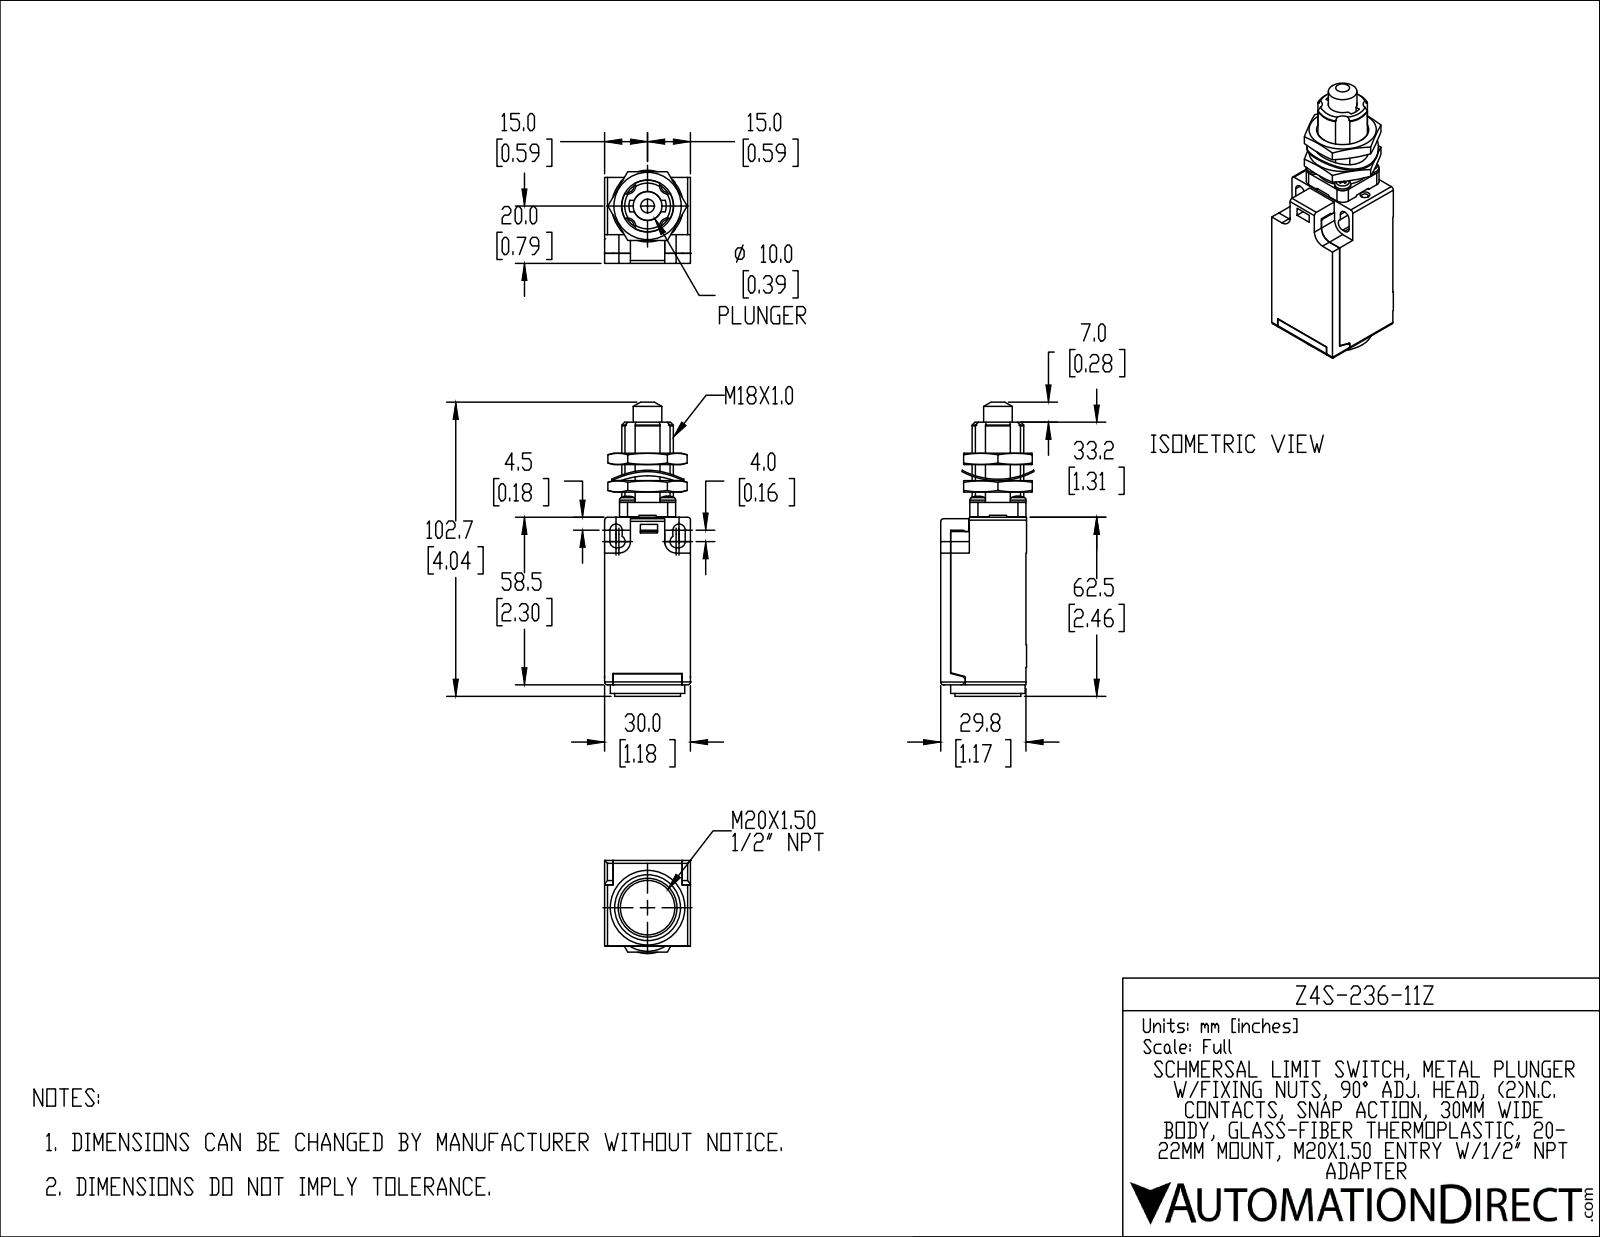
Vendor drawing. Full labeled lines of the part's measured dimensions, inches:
Part name (STEP PRODUCT): Z4S-236-11Z
STEP written by: SolidWorks 2019 (AUTOMOTIVE_DESIGN)
Units: inches
Bodies: 4 solids, 348 faces (226 planar, 90 cylindrical, 32 other)
Overall size (bounding box): 4.043 × 1.279 × 1.181
Volume: 3.526 in³ · Surface area: 31.42 in²
Round holes (diameter × count): ⌀0.094 ×6, ⌀0.126 ×4, ⌀0.512 ×1, ⌀0.545 ×1, ⌀0.732 ×1, ⌀0.748 ×1
Round bosses / shafts (diameter × count): ⌀0.213 ×4, ⌀1.024 ×1, ⌀0.984 ×1, ⌀0.906 ×1, ⌀0.415 ×1, ⌀0.394 ×1, ⌀0.248 ×1
Partial cylindrical surfaces — rounded edges, fillets, slot ends (radius × count): R0.039 ×6, R0.085 ×6, R0.11 ×4, R0.11 ×4, R0.157 ×2, R1.043 ×2, R0.024 ×1, R0.059 ×1
Main face-to-face distances: 1.181, 0.138, 1.035, 1.173, 0.157, 1.043, 0.087, 0.079, 2.067, 0.118
Hole centre spacings: 0.317, 0.39, 0.551, 0.76, 0.308, 0.433, 0.454, 0.497
